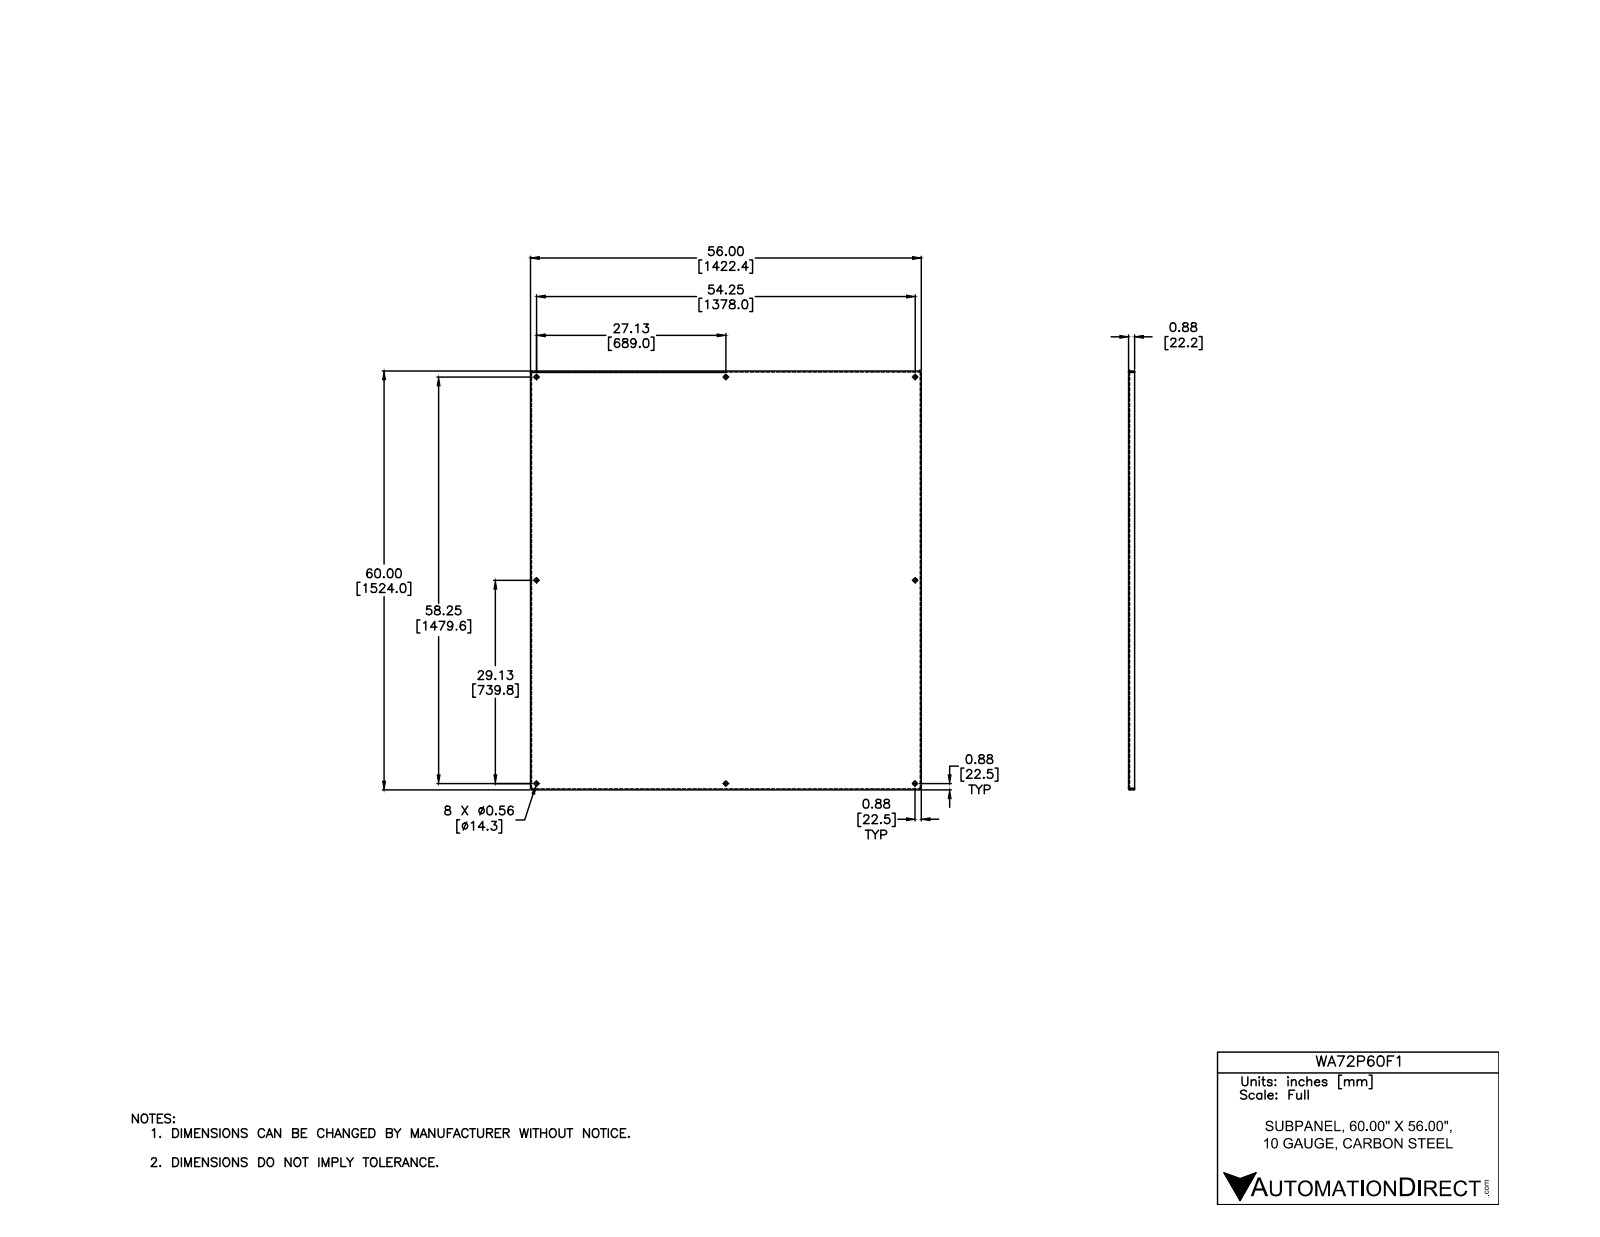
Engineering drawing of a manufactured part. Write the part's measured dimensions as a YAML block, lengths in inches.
part_name: "WA_P_F"
step_written_by: "Autodesk Inventor 2012 (AUTOMOTIVE_DESIGN)"
units: inches
bodies: {solids: 1, faces: 46, planar: 22, cylindrical: 16, other: 8}
overall_size: [60, 56, 0.875]
volume: 440.2
surface_area: 7074
round_holes:
  - {diameter: 0.563, count: 8}
partial_cylinders:
  - {radius: 0.031, count: 4}
  - {radius: 0.156, count: 4}
face_to_face_distances: [0.125, 0.125, 55.875, 56, 55.75, 59.875, 60, 59.75, 59.875, 0.75]
hole_center_spacings: [27.125, 29.125, 39.8, 54.25, 58.25, 61.574, 61.574, 64.256]
